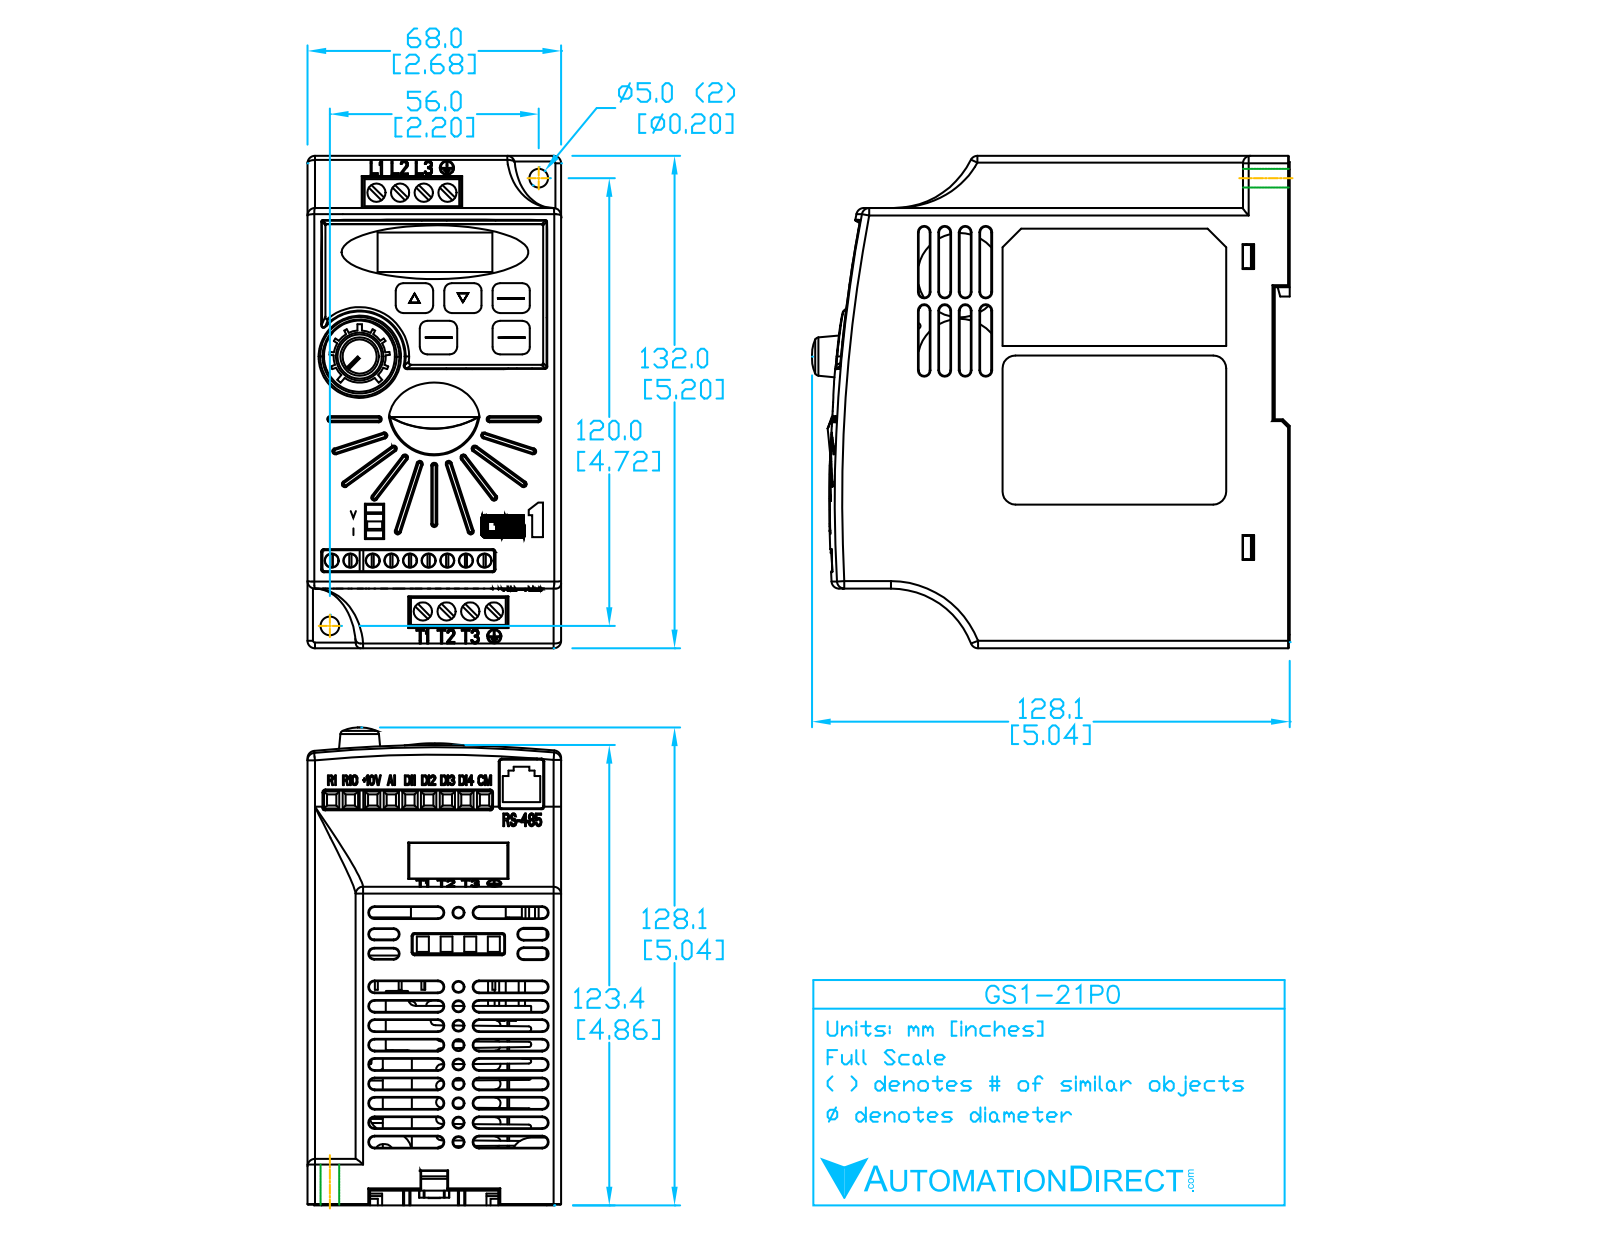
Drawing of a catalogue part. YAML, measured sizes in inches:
part_name: "GS1-21P0"
step_written_by: "SolidWorks 2015 (AUTOMOTIVE_DESIGN)"
units: inches
bodies: {solids: 1, faces: 885, planar: 536, cylindrical: 168, other: 181}
overall_size: [5.285, 5.2, 2.68]
volume: 61.51
surface_area: 109.5
round_holes:
  - {diameter: 0.15, count: 9}
  - {diameter: 0.187, count: 8}
  - {diameter: 0.2, count: 2}
round_bosses_or_shafts:
  - {diameter: 0.316, count: 5}
partial_cylinders:
  - {radius: 0.03, count: 38}
  - {radius: 0.1, count: 22}
  - {radius: 0.06, count: 20}
  - {radius: 0.063, count: 6}
  - {radius: 0.015, count: 2}
  - {radius: 0.093, count: 2}
  - {radius: 0.2, count: 2}
  - {radius: 0.44, count: 2}
face_to_face_distances: [2.68, 0.175, 5.2, 0.015, 5.185, 0.167, 0.55, 4.65, 0.535, 0.62]
hole_center_spacings: [0.2, 0.4, 0.6, 0.8, 1, 1.2, 1.4, 3.921]
